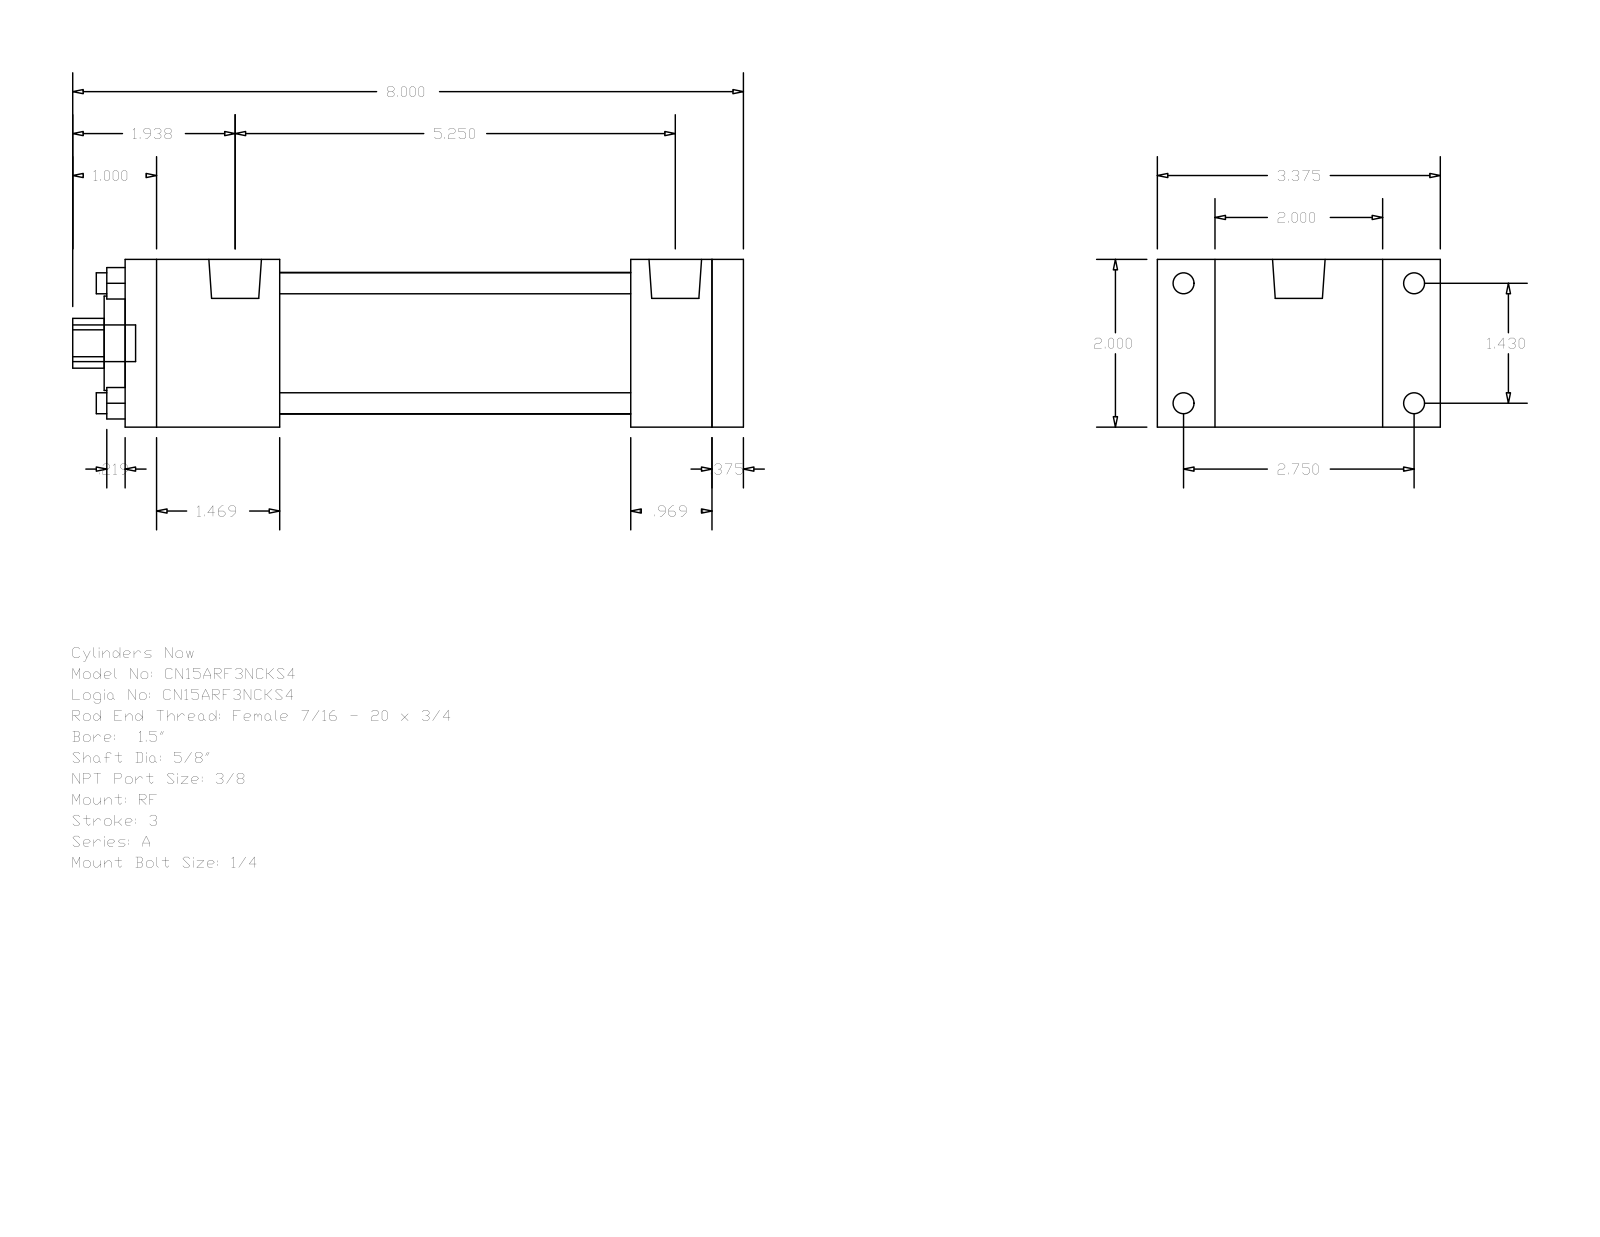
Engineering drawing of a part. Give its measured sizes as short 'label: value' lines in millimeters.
name: A_RF__0150_0.625
written by: GSSL Pune (CONFIG_CONTROL_DESIGN)
unit: mm
bodies: 0 solids, 92 faces (64 planar, 28 cylindrical, 0 other)
size: 203.2 × 85.72 × 50.8
holes: 4× ⌀6.35, 1× ⌀15.88, 1× ⌀28.57, 1× ⌀42.93
bosses: 4× ⌀6.35, 4× ⌀5.56, 2× ⌀15.93, 1× ⌀11.11
rounds: 1× R7.54
face distances: 50.8, 9.52, 177.8, 187.32, 153.19, 24.61, 34.13, 46.83, 106.36, 130.97
hole spacings: 25.68, 36.32, 51.36
